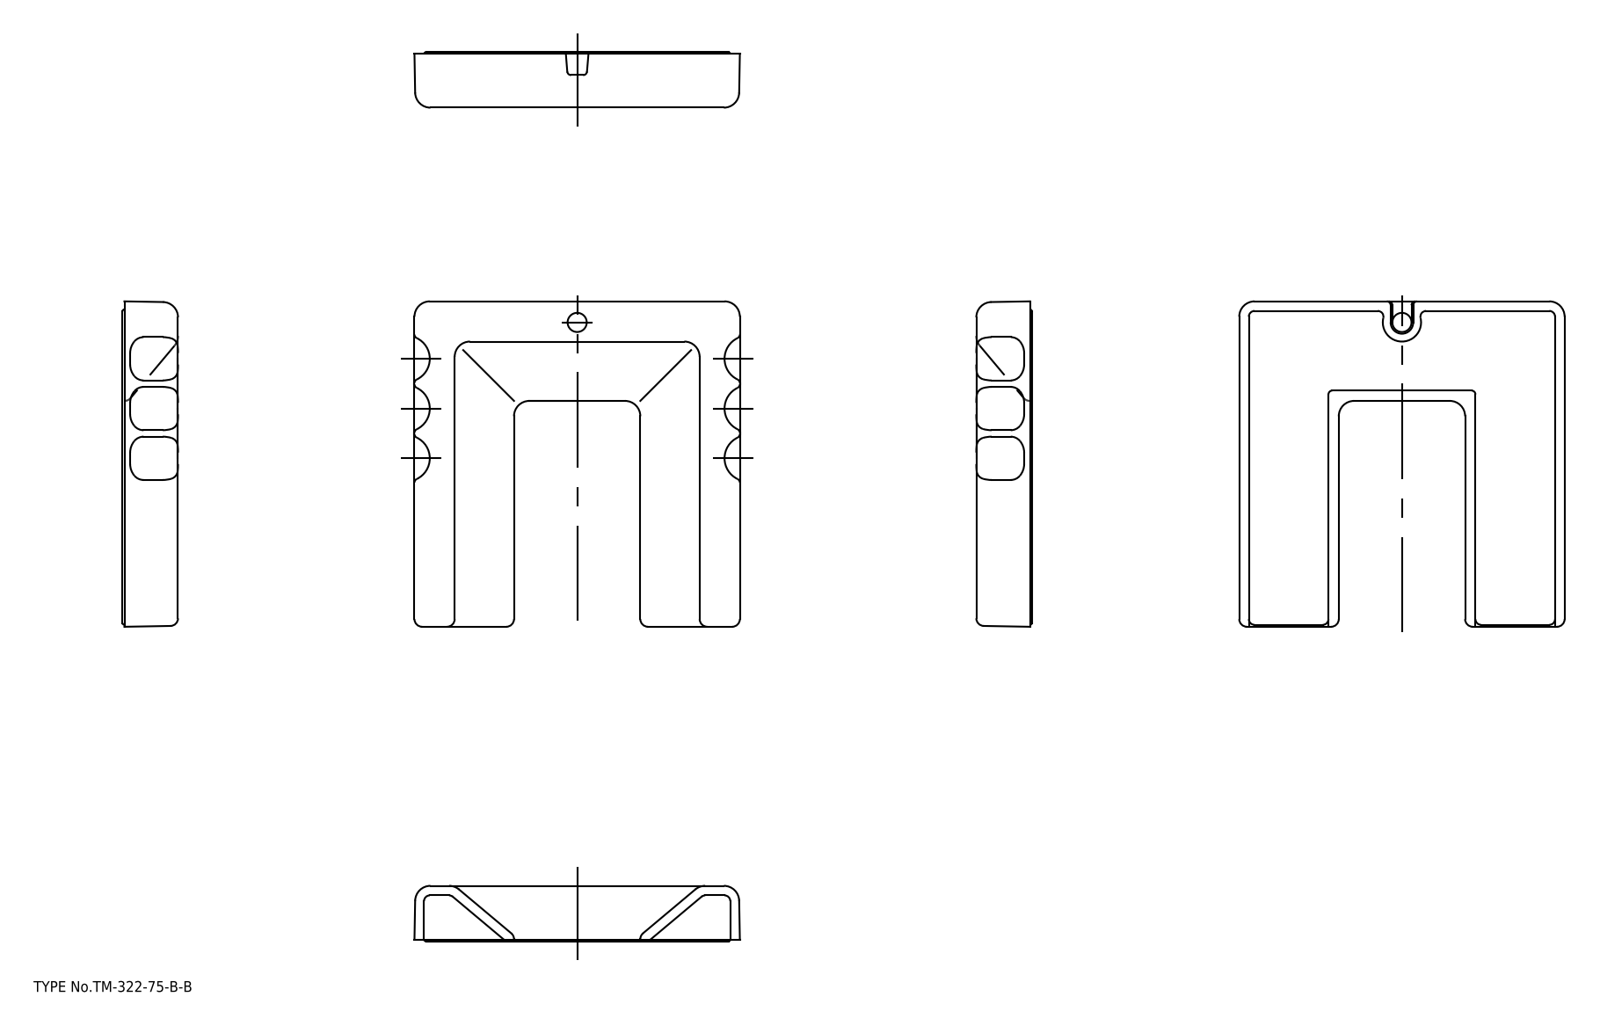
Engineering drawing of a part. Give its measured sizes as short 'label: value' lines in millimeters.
name: TM_322_75; PC14-prt0; PC14-prt1; PC14-prt2 (+3 more)
written by: spGate 16.7.1 (AUTOMOTIVE_DESIGN)
unit: mm
bodies: 0 solids, 196 faces (50 planar, 71 cylindrical, 75 other)
size: 85 × 85 × 14.5
holes: 1× ⌀5
rounds: 12× R4, 10× R2, 9× R1, 8× R1.5, 7× R0.5, 6× R6, 1× R5
face distances: 1, 0.5, 13.5, 14, 14.5, 20.8, 59.2, 80, 82.5, 82
